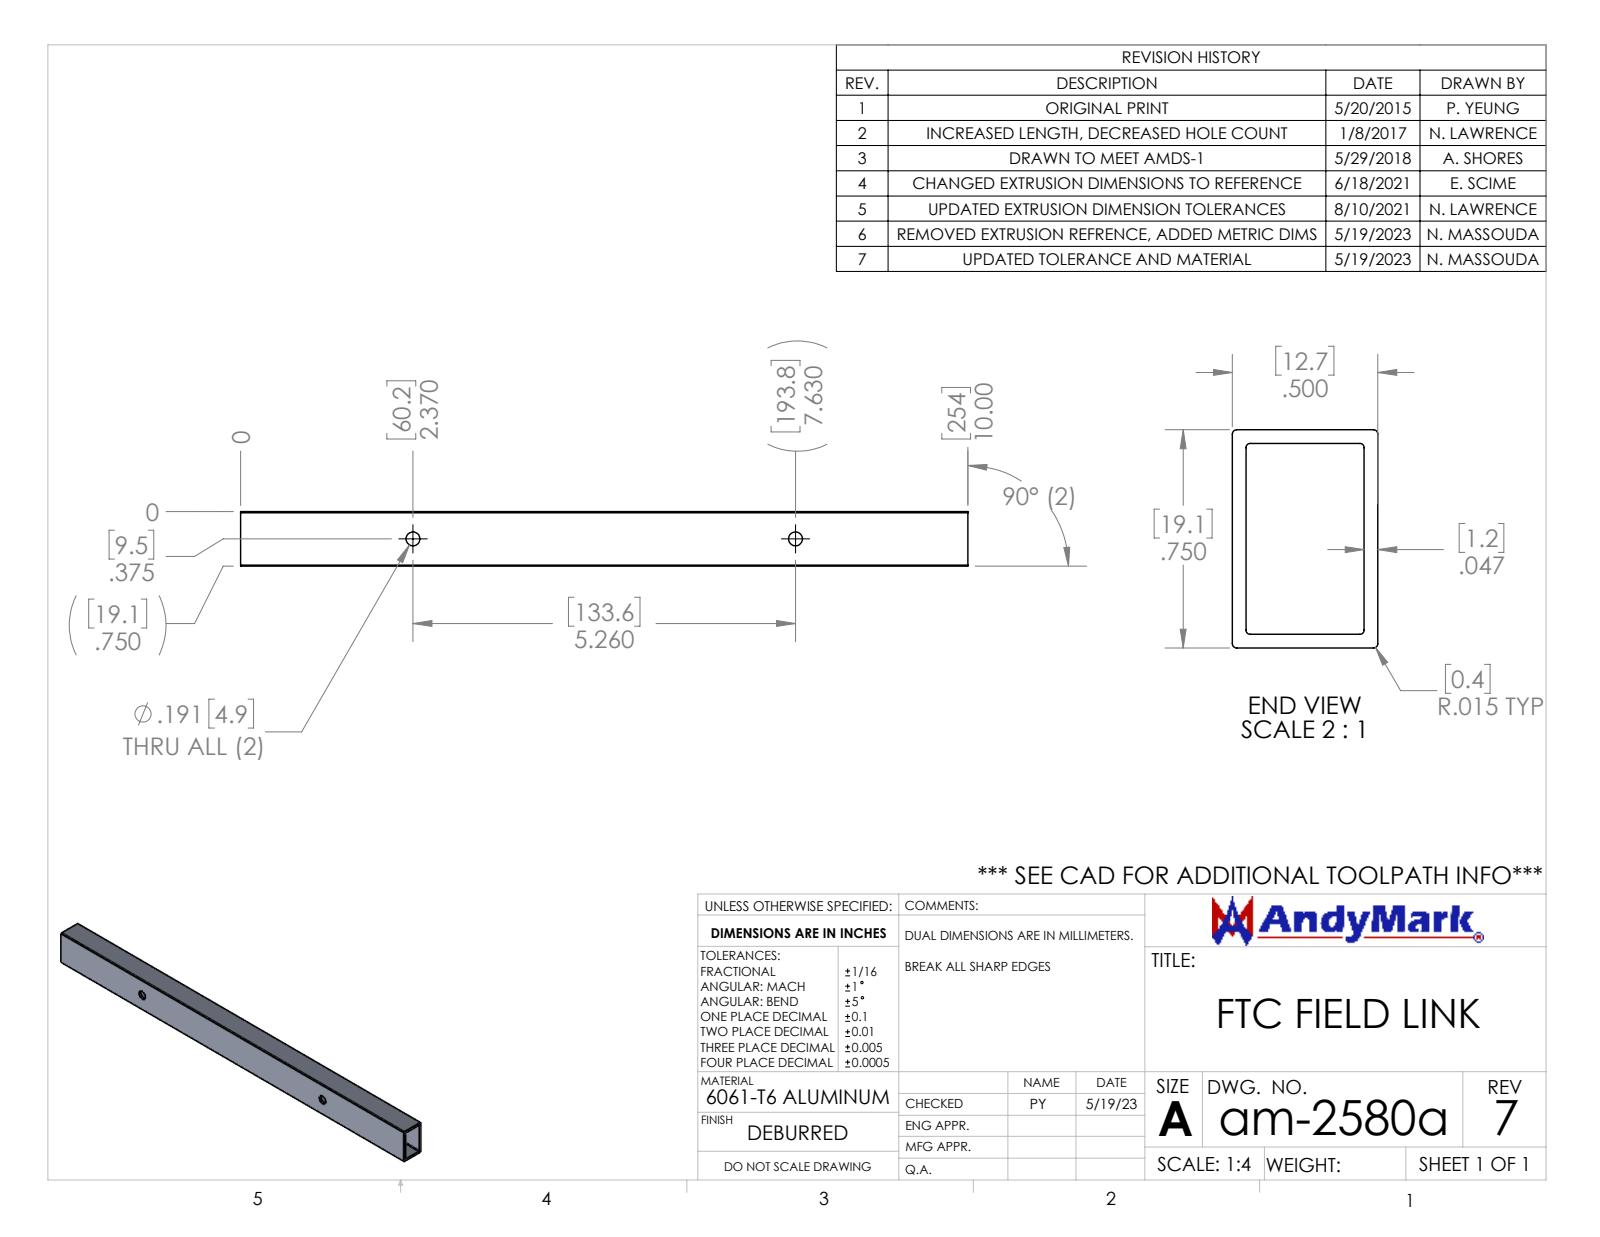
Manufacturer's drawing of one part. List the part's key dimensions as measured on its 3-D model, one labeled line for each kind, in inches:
Part name (STEP PRODUCT): SAPA IAH-821
STEP written by: SolidWorks 2022 (CONFIG_CONTROL_DESIGN)
Units: inches
Bodies: 1 solid, 26 faces (10 planar, 16 cylindrical, 0 other)
Overall size (bounding box): 10 × 0.75 × 0.5
Volume: 1.081 in³ · Surface area: 45.83 in²
Round holes (diameter × count): ⌀0.191 ×2
Partial cylindrical surfaces — rounded edges, fillets, slot ends (radius × count): R0.015 ×8
Main face-to-face distances: 0.047, 0.453, 0.5, 0.406, 0.75, 0.047, 0.703, 0.656, 0.703, 10
Hole centre spacings: 5.26
